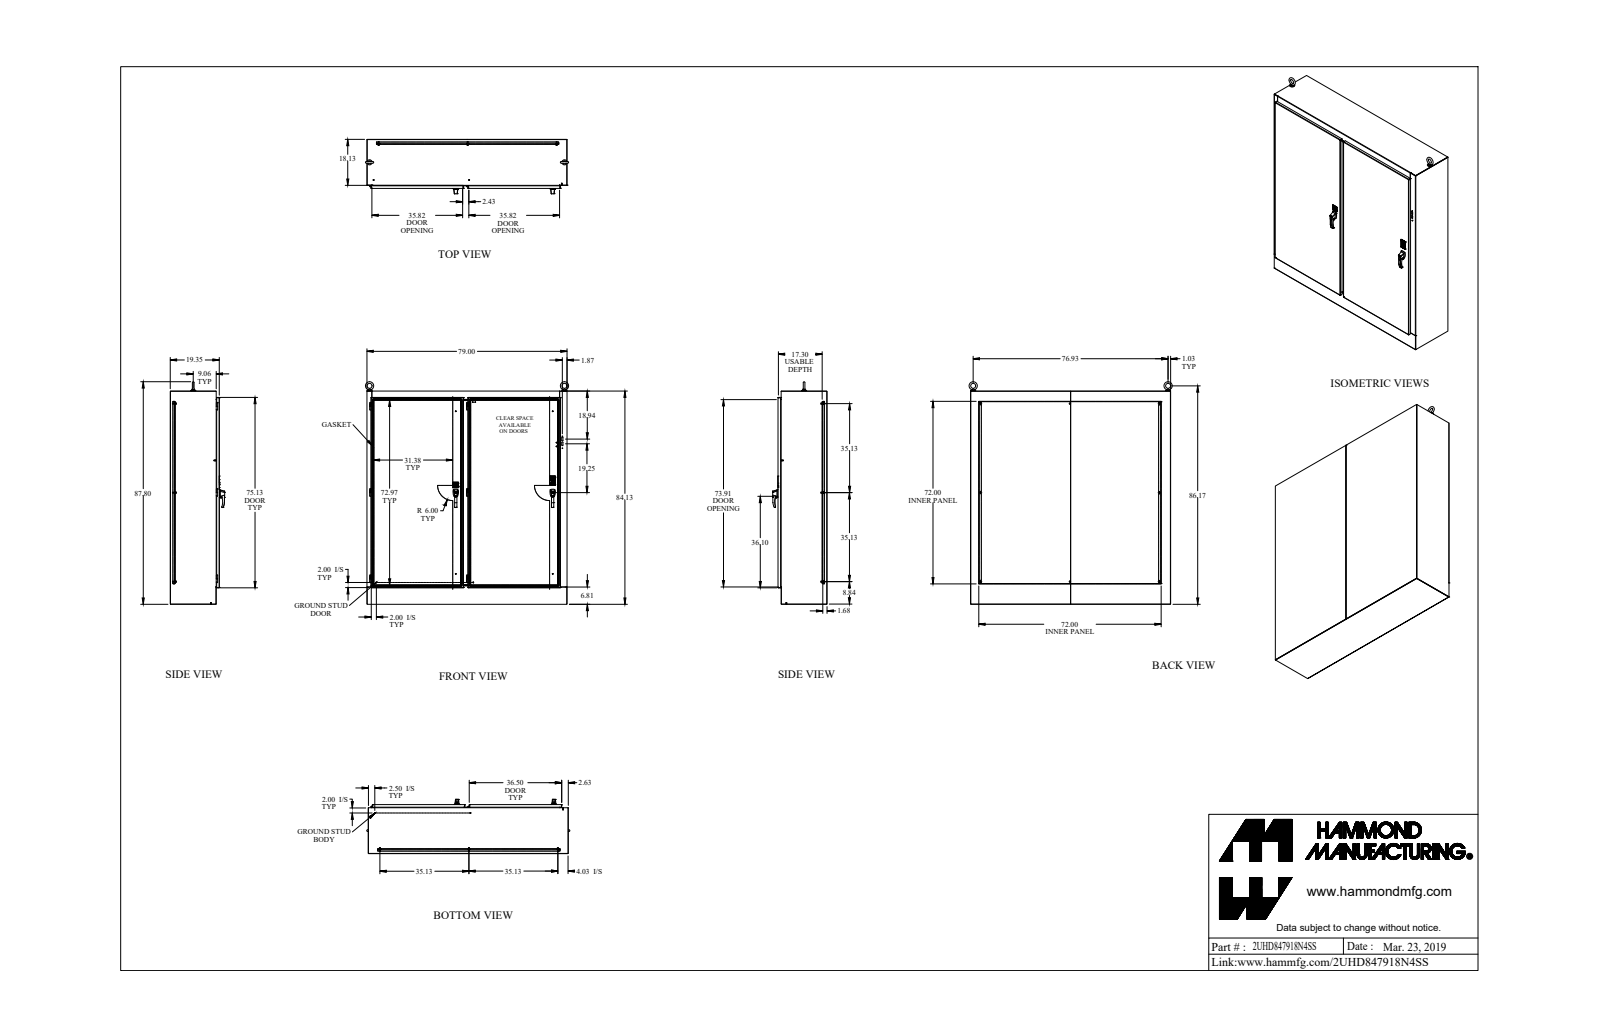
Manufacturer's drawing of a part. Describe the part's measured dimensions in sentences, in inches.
The part is named "2UHD847918N4SS". Its 3-D file was written by "SolidWorks 2018 (AUTOMOTIVE_DESIGN)". It is 223 solids with 3338 faces: 1961 planar, 990 cylindrical and 387 other. Overall it measures 87.799 by 80.182 by 21.466 inches. Its volume is 5 051 cubic inches and its surface area 58 238 square inches. Round holes: 13 of diameter 0.196, 12 of diameter 0.25, 9 of diameter 0.281, 9 of diameter 0.307, 8 of diameter 0.35, 6 of diameter 0.255, 6 of diameter 0.257, 6 of diameter 0.313, 5 of diameter 0.201, 5 of diameter 0.313, 5 of diameter 0.445, 4 of diameter 0.156. Round bosses or shafts: 18 of diameter 0.25, 12 of diameter 1, 9 of diameter 0.65, 9 of diameter 0.375, 8 of diameter 0.332, 6 of diameter 0.75, 6 of diameter 0.625, 6 of diameter 0.5. Partial cylindrical surfaces (rounded edges, fillets, slot ends): 67 of radius 0.125, 42 of radius 0.5, 35 of radius 0.06, 32 of radius 0.017, 30 of radius 0.048, 30 of radius 0.143, 28 of radius 0.03, 26 of radius 0.25. The main face-to-face distances are 0.095, 0.072, 17.461, 19.368, 19.273, 1.907, 1.812, 1.741, 1.835, 17.533. The hole center spacings are 38.25, 1, 1.287, 1.72, 3.43, 30.937, 33.188, 38.267.
